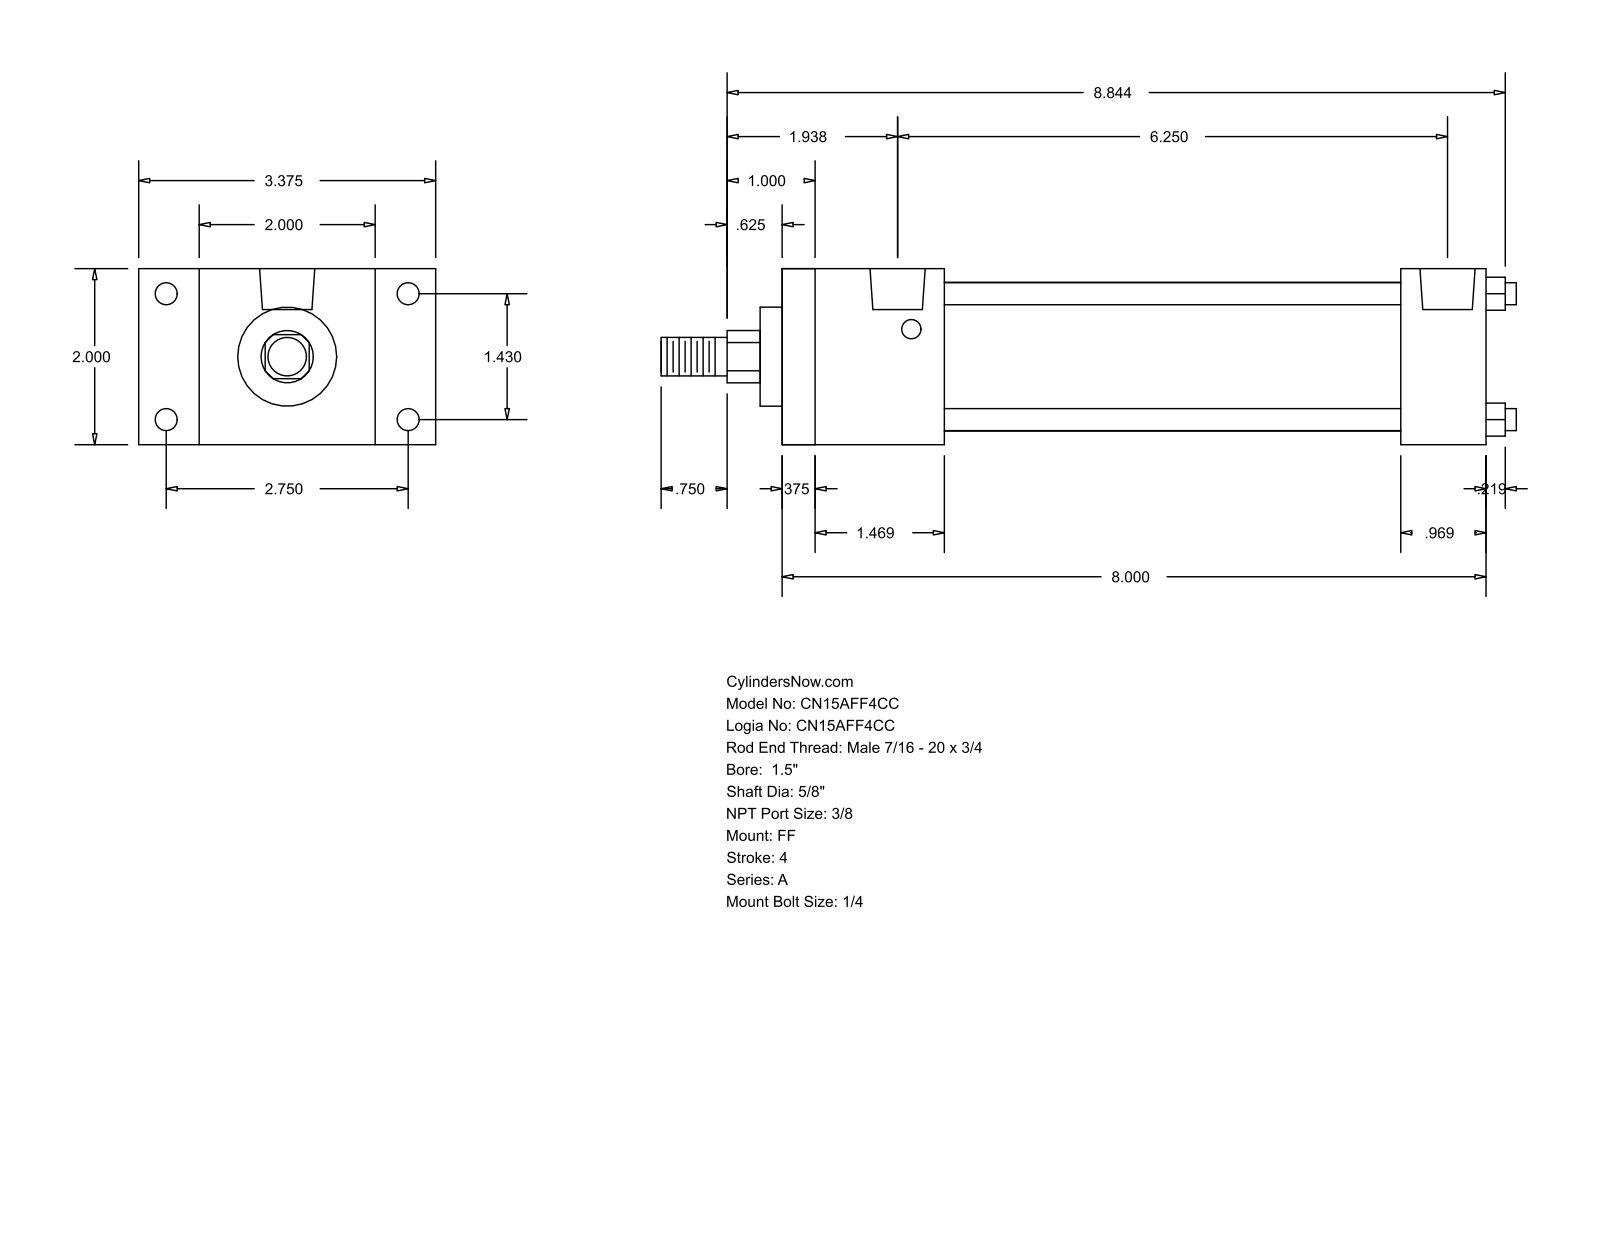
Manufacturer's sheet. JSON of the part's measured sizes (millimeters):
{"part_name": "A_FF__0150_0.625", "step_written_by": "GSSL Pune (CONFIG_CONTROL_DESIGN)", "units": "millimeters", "bodies": {"solids": 0, "faces": 92, "planar": 64, "cylindrical": 28, "other": 0}, "overall_size": [246.86, 85.72, 50.8], "round_holes": [[5.56, 4], [6.35, 4], [15.93, 2]], "round_bosses_or_shafts": [[6.35, 4], [42.93, 1], [28.57, 1], [15.88, 1], [11.11, 1]], "partial_cylinders_radius": [[7.54, 1]], "face_to_face_distances": [50.8, 203.19, 9.52, 193.67, 46.83, 178.59, 37.31, 169.07, 131.76, 156.36], "hole_center_spacings": [3.97, 36.32, 69.84, 78.72, 150.81, 154.78, 158.75]}
